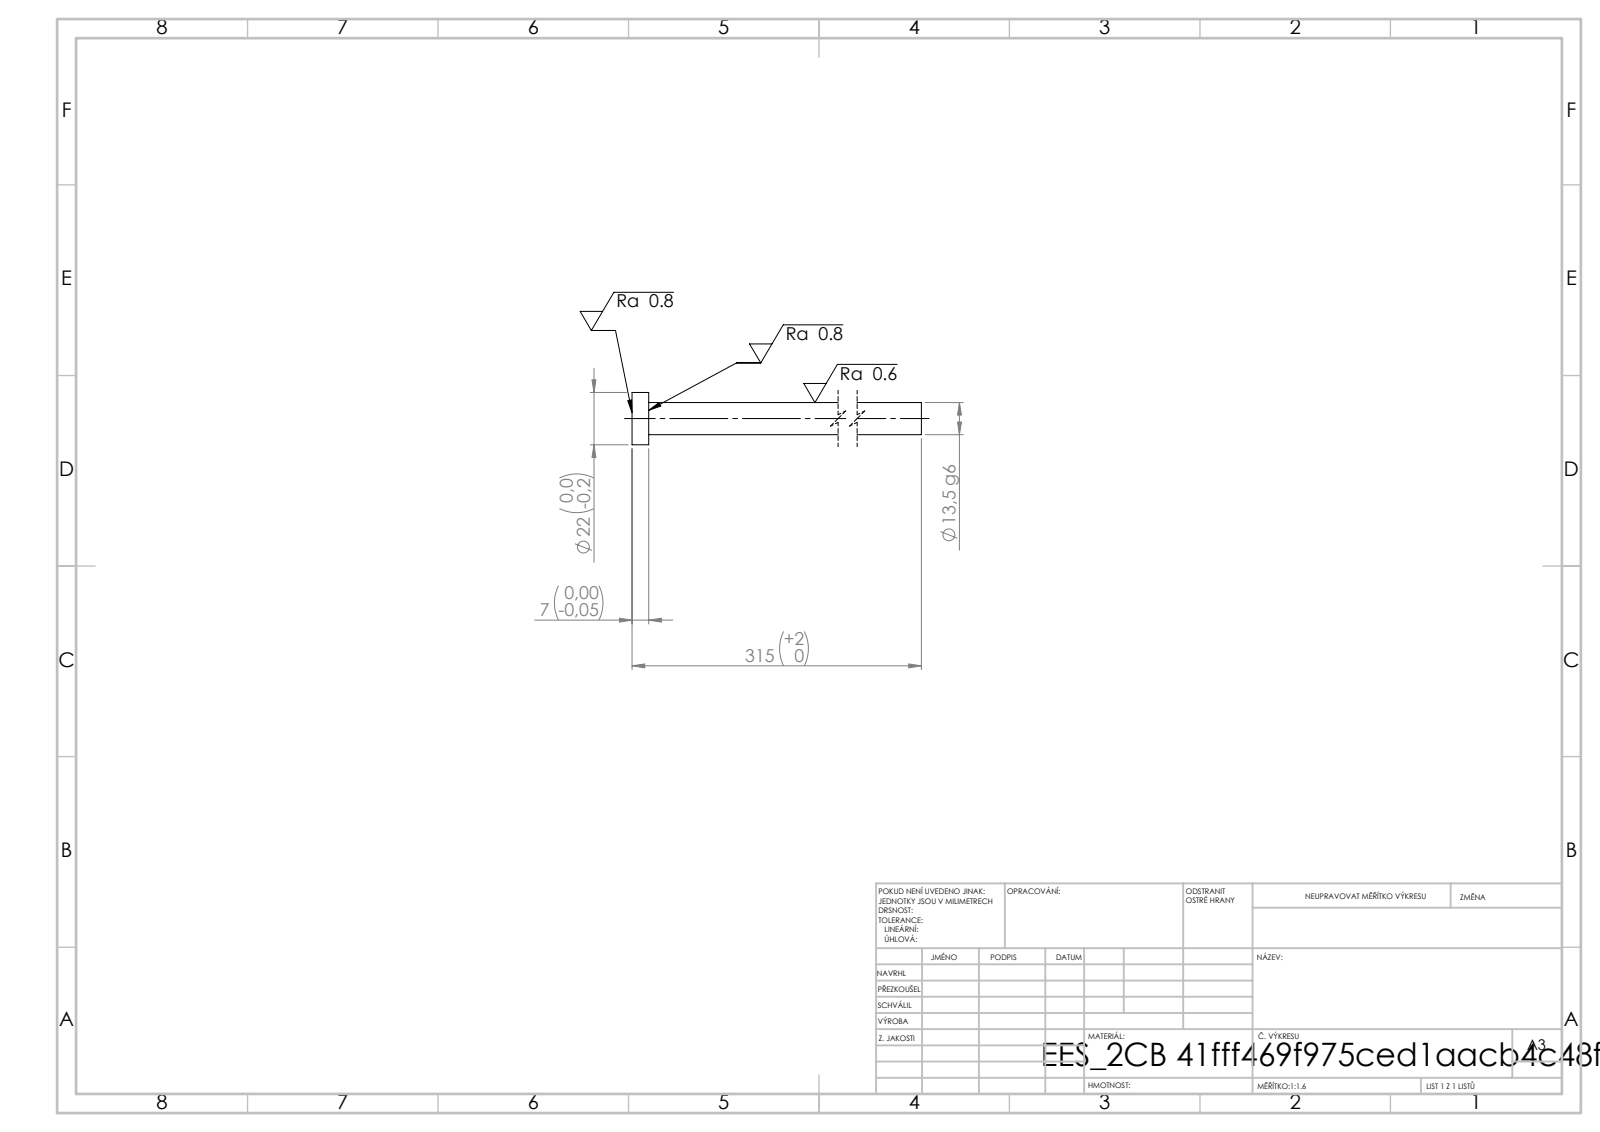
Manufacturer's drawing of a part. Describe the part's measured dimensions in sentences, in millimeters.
Its 3-D file was written by "SolidWorks 2019 (CONFIG_CONTROL_DESIGN)". It is 1 solid with 7 faces: 3 planar, 4 cylindrical and 0 other. Overall it measures 315 by 22 by 22 millimeters. Its volume is 46 748 cubic millimeters and its surface area 14 307 square millimeters. Round bosses or shafts: 1 of diameter 22, 1 of diameter 13.5. The main face-to-face distances are 7, 315, 308.
